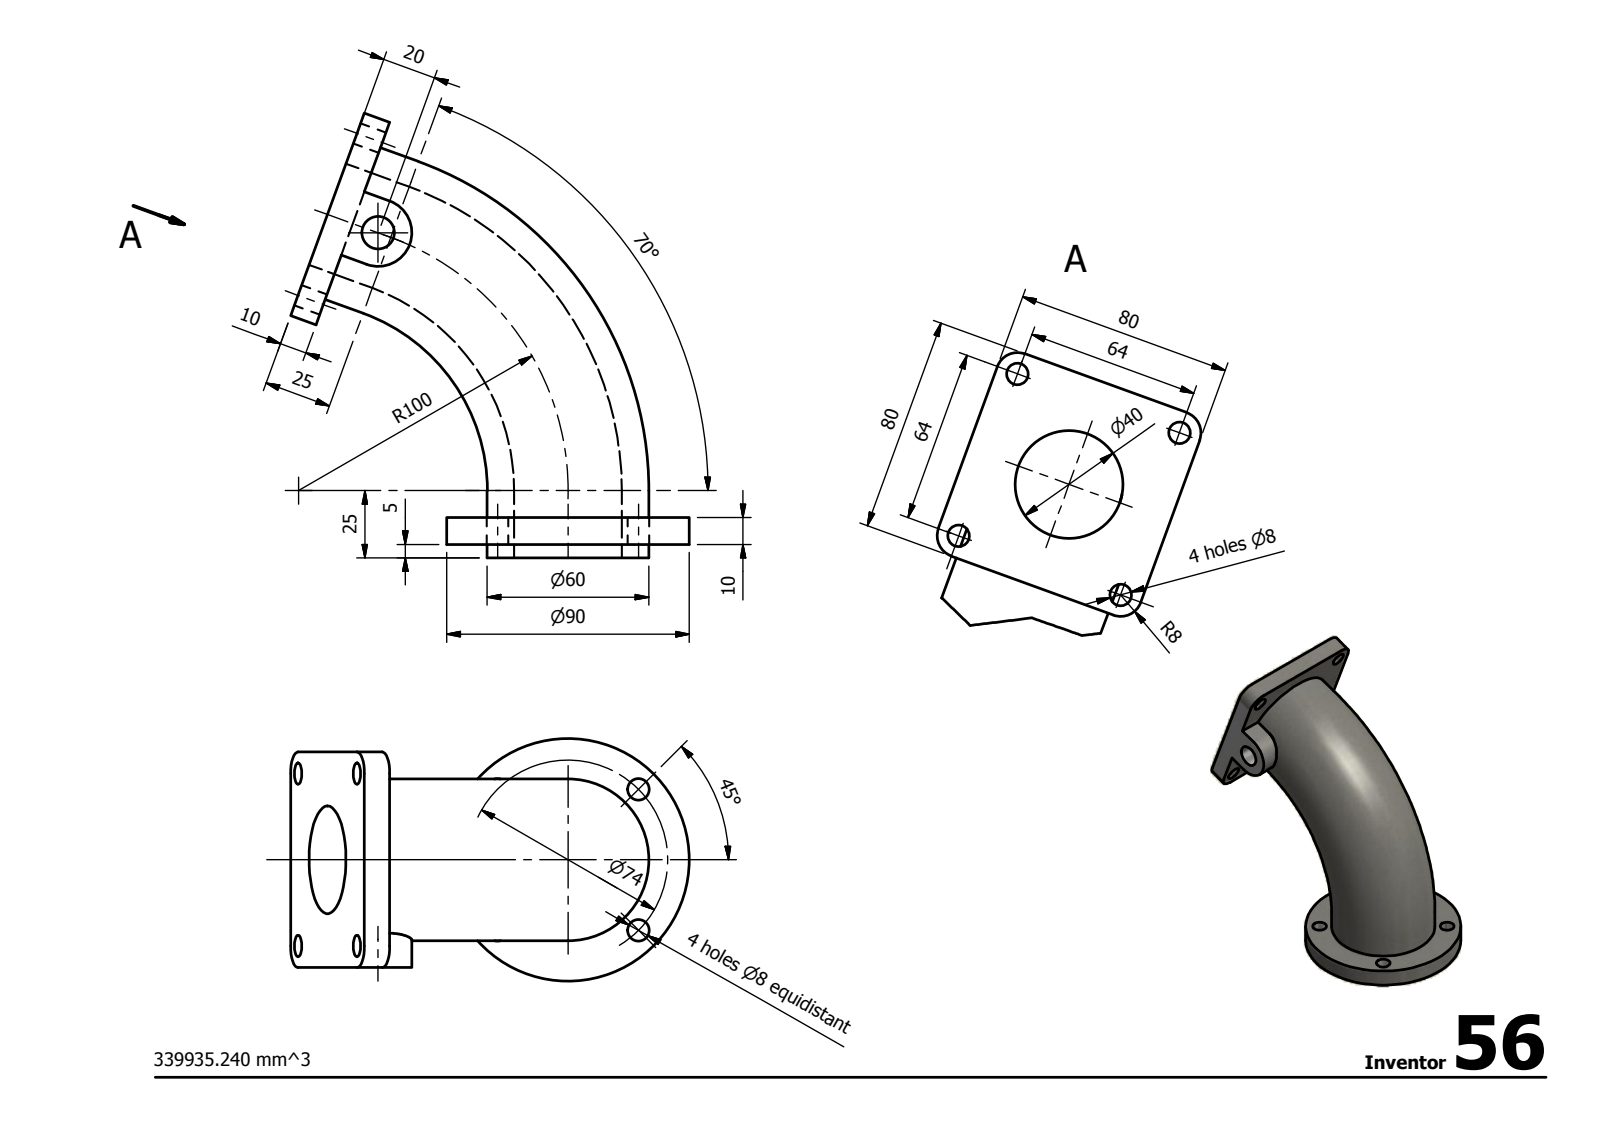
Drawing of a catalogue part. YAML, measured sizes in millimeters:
step_written_by: "Autodesk Inventor 2014 (AUTOMOTIVE_DESIGN)"
units: millimeters
bodies: {solids: 1, faces: 33, planar: 11, cylindrical: 20, other: 2}
overall_size: [165.11, 147.97, 90]
volume: 340000
surface_area: 75620
round_holes:
  - {diameter: 8, count: 8}
  - {diameter: 40, count: 2}
  - {diameter: 12, count: 1}
round_bosses_or_shafts:
  - {diameter: 60, count: 2}
  - {diameter: 90, count: 1}
partial_cylinders:
  - {radius: 8, count: 4}
  - {radius: 12.5, count: 1}
face_to_face_distances: [10, 5, 15, 80, 80.02, 27.51, 52.51, 25]
hole_center_spacings: [37, 52.32, 64, 45.23, 45.28, 73.99, 90.51]
